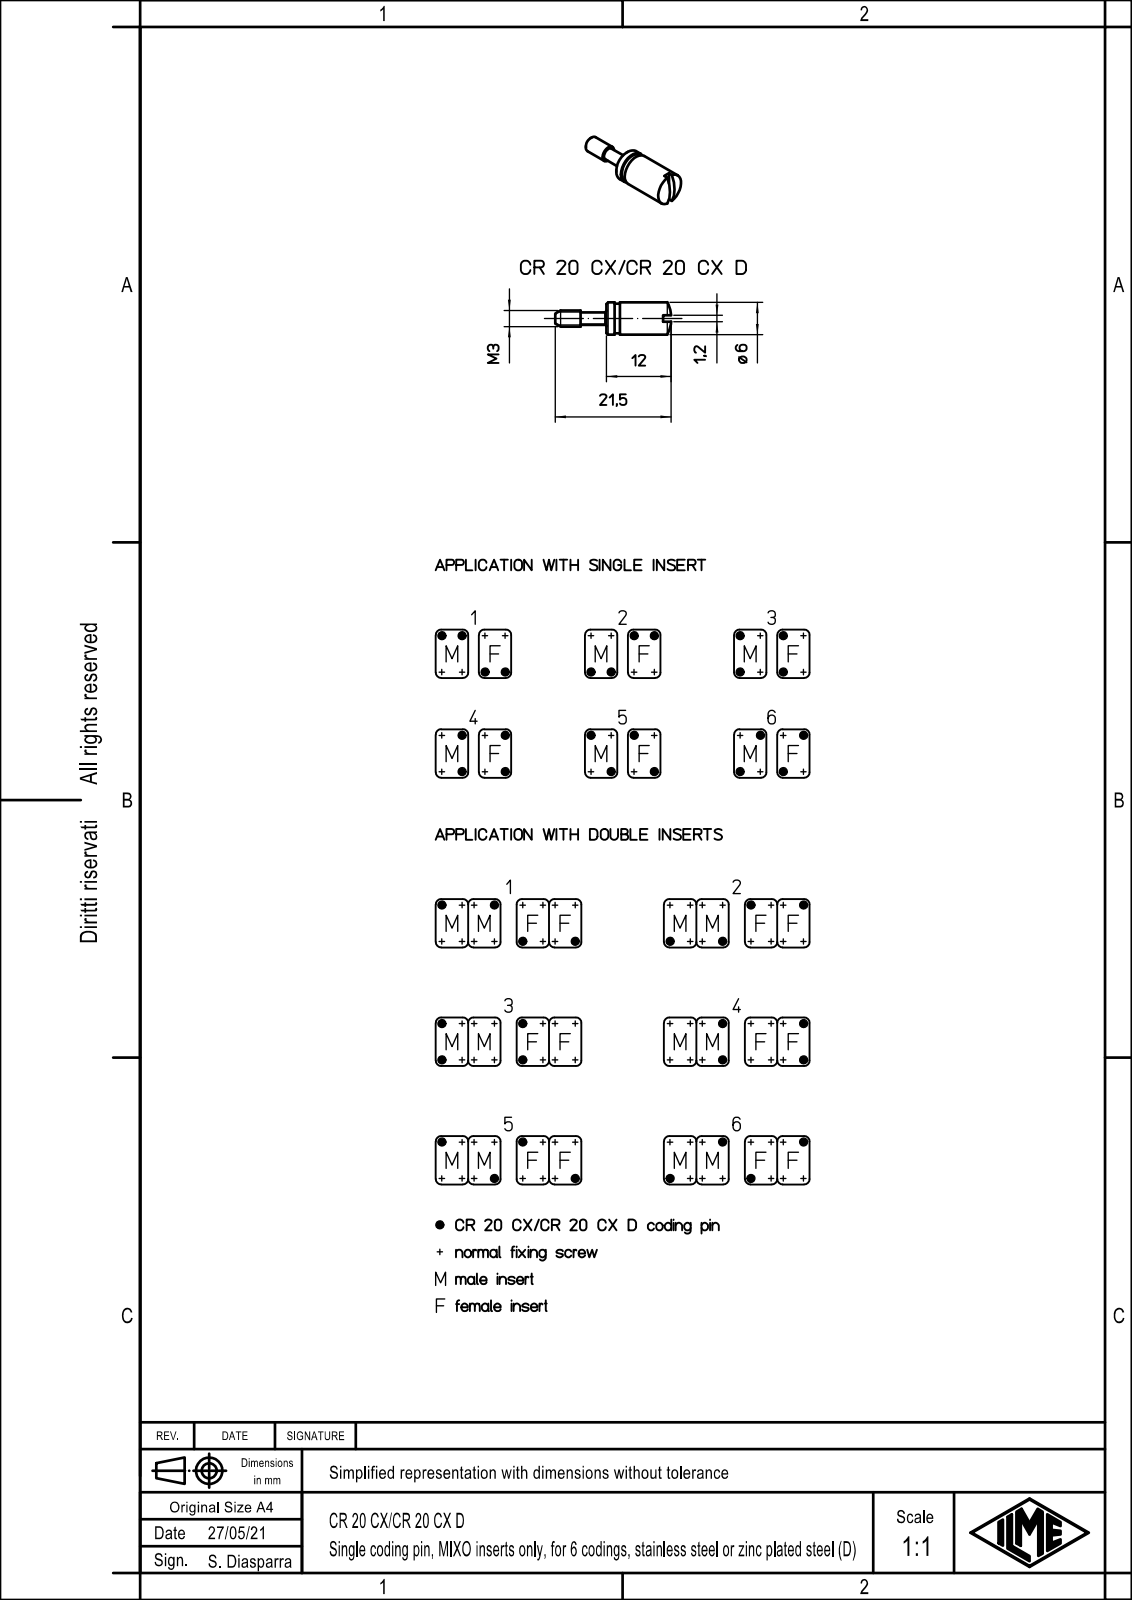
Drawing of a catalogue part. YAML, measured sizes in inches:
part_name: "CR 20 CX"
step_written_by: "Autodesk Inventor 7 (AUTOMOTIVE_DESIGN)"
units: inches
bodies: {solids: 1, faces: 21, planar: 5, cylindrical: 6, other: 10}
overall_size: [0.864, 0.236, 0.236]
volume: 0.023
surface_area: 0.572
round_bosses_or_shafts:
  - {diameter: 0.236, count: 1}
  - {diameter: 0.118, count: 1}
  - {diameter: 0.098, count: 1}
face_to_face_distances: [0.413, 0.079, 0.394, 0.807]
